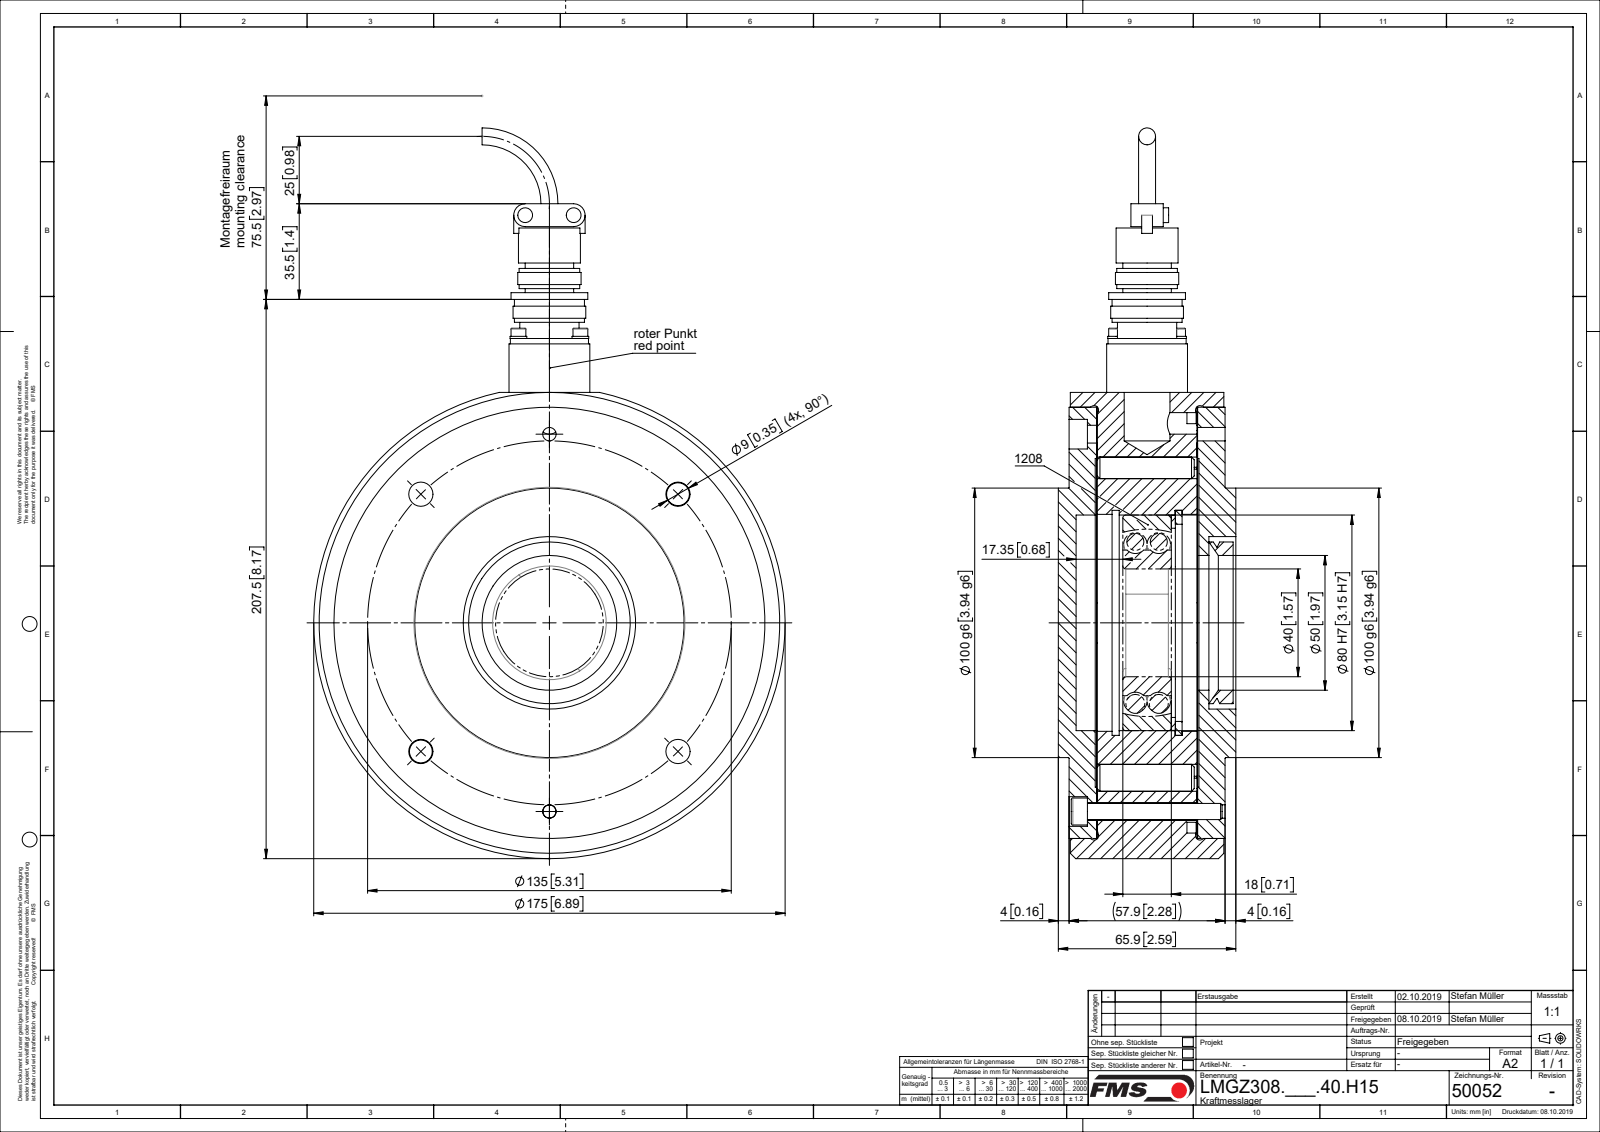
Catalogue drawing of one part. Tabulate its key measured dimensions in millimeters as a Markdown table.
| quantity | value |
| --- | --- |
| part name | L50052; L49015; ~TEIL1; L49026 (+8 more) |
| STEP written by | Mechanical Desktop 2007 (CONFIG_CONTROL_DESIGN) |
| units | millimeters |
| bodies | 21 solids, 378 faces (101 planar, 229 cylindrical, 48 other) |
| overall size | 271.15 × 175 × 65.9 |
| volume | 1 269 000 mm³ |
| surface area | 272 603 mm² |
| round holes (diameter × count) | 2.6 × 4, 3.2 × 4, 3.4 × 4, 9 × 4, 5.15 × 2, 6.6 × 2, 8.68 × 2, 11 × 2, 23 × 1, 40 × 1, 48 × 1, 50 × 1 |
| round bosses / shafts (diameter × count) | 5.5 × 6, 6.2 × 4, 3 × 4, 2.5 × 4, 175 × 1, 160 × 1, 100 × 1, 58 × 1 |
| partial cylindrical surfaces (radius × count) | 4.25 × 2, 7.5 × 2 |
| main face-to-face distances | 37.25, 10.2, 10.45, 47.45, 47.7, 37, 37.5, 0.5, 38, 9.75 |
| hole center spacings | 16.26, 23, 52.67, 67.5, 95.46, 127.04, 32.53, 70 |
